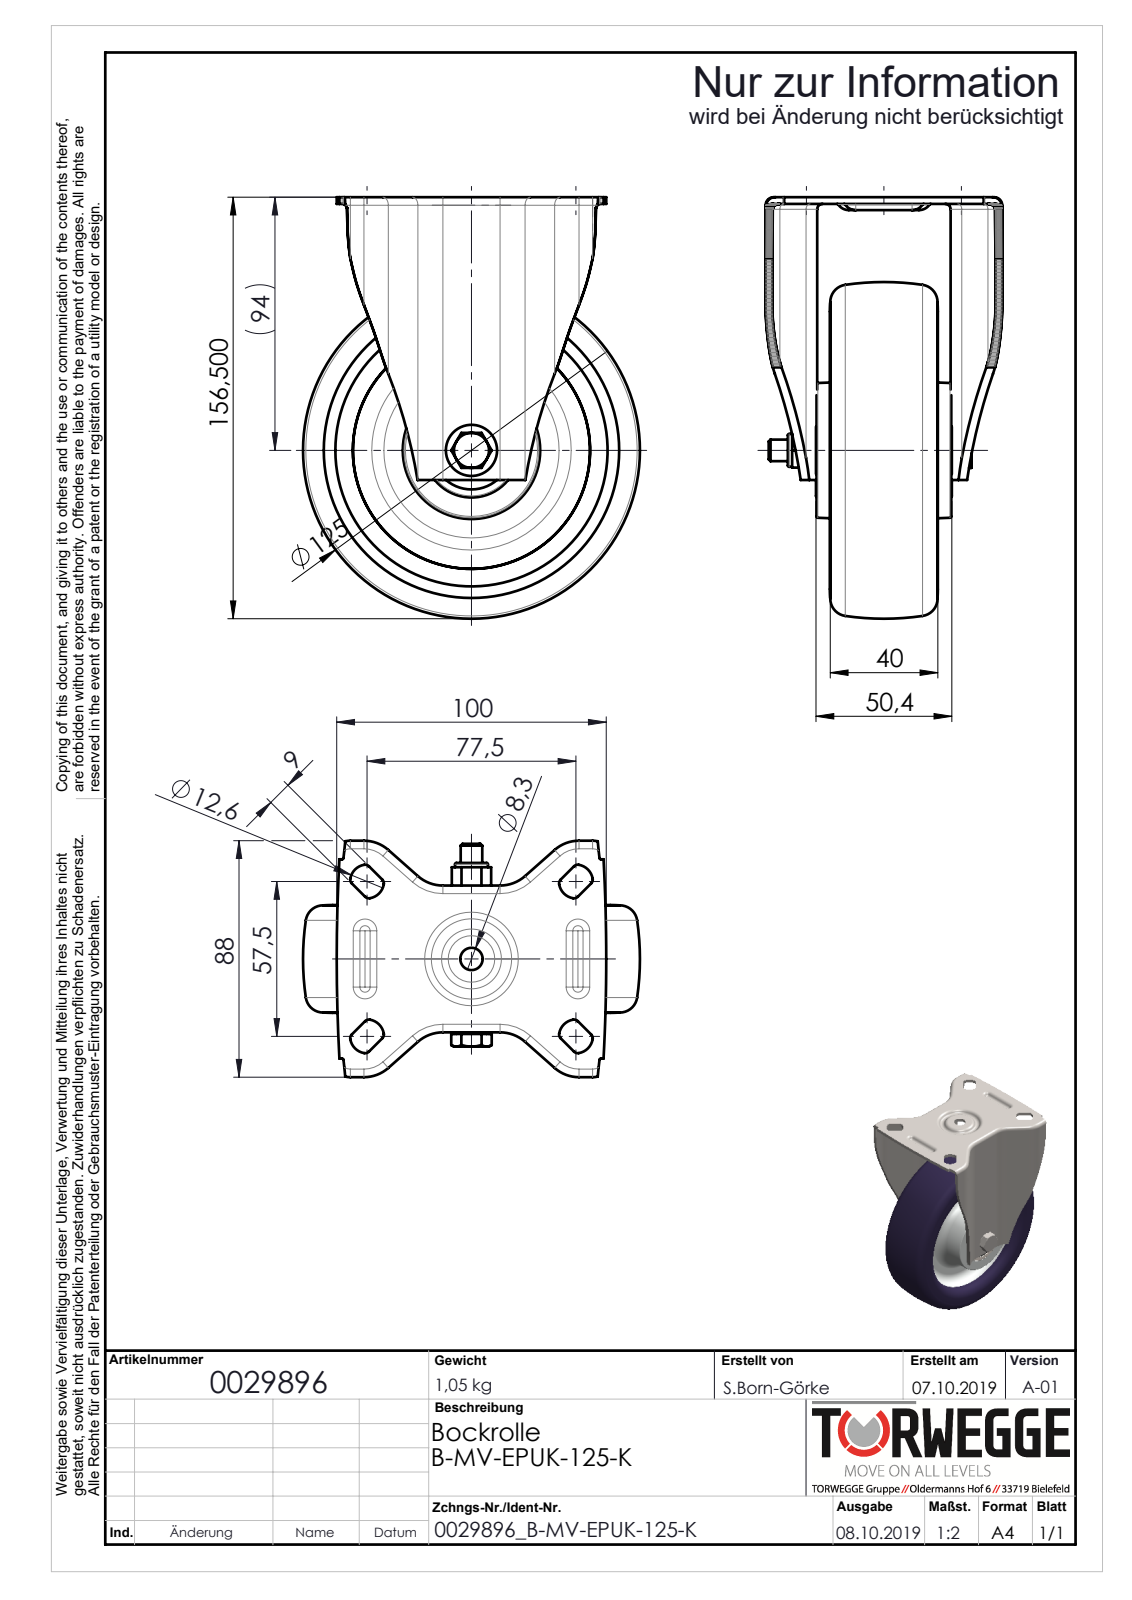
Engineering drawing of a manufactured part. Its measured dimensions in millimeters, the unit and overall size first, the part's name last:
Units: millimetres
Overall size (bounding box): 156.5 × 125 × 87.8
Round holes (diameter × count): ⌀6.65 ×1, ⌀8.2 ×1, ⌀8.3 ×1, ⌀15 ×1, ⌀16 ×1, ⌀21 ×1, ⌀29 ×1, ⌀30 ×1, ⌀88 ×1
Round bosses / shafts (diameter × count): ⌀51 ×1, ⌀35 ×1, ⌀20 ×1, ⌀13 ×1, ⌀12.2 ×1, ⌀8 ×1
Partial cylindrical surfaces — rounded edges, fillets, slot ends (radius × count): R2 ×24, R3 ×12, R0.5 ×8, R5 ×4, R6.3 ×4, R7.5 ×4, R11.15 ×4, R13.65 ×4
Main face-to-face distances: 2.5, 17.22, 52, 19.72, 14.25, 40.25, 11.75, 37.75, 54.5, 20
Volume: 419 680 mm³ · Surface area: 165 496 mm²
Bodies: 18 solids, 1441 faces (930 planar, 199 cylindrical, 312 other)
Part name (STEP PRODUCT): 0029896_B-MV-EPUK-125-K_(A-01)
STEP written by: SolidWorks 2018 (AUTOMOTIVE_DESIGN)
